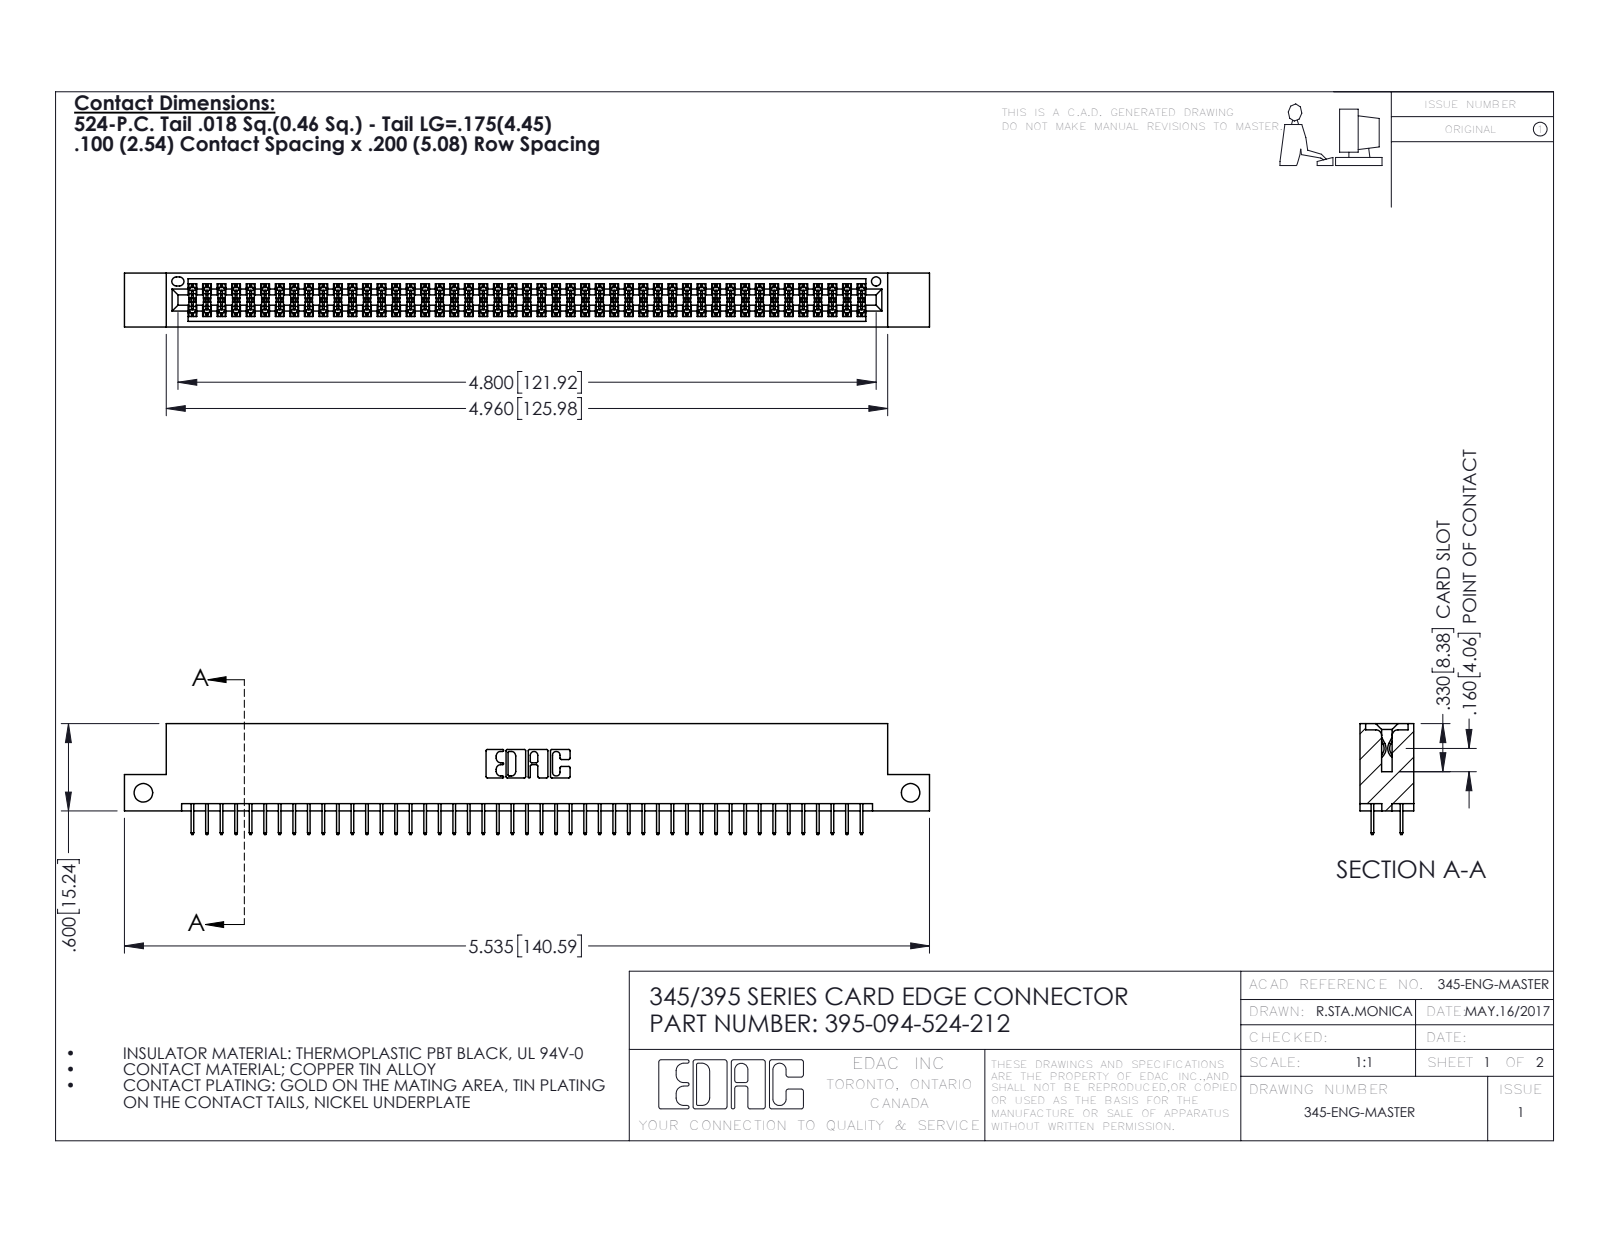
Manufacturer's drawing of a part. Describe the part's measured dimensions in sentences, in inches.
The part is named "395-094-524-212; 345 Part_Flush Mounting Lugs - Side Mount; 345-292-001_345-293-124". Its 3-D file was written by "SolidWorks 2016 (CONFIG_CONTROL_DESIGN)". It is 95 solids with 5202 faces: 3746 planar, 1456 cylindrical and 0 other. Overall it measures 5.535 by 0.762 by 0.37 inches. Its volume is 0.822 cubic inches and its surface area 30.23 square inches. Round holes: 2 of diameter 0.128, 1 of diameter 0.064. Partial cylindrical surfaces (rounded edges, fillets, slot ends): 141 of radius 0.006, 22 of radius 0.01, 6 of radius 0.007, 6 of radius 0.031, 3 of radius 0.026, 2 of radius 0.014, 2 of radius 0.019, 2 of radius 0.022. The main face-to-face distances are 0.298, 0.072, 0.2, 0.37, 0.098, 0.272, 0.025, 0.225, 0.072, 0.175. The hole center spacings are 5.275.
